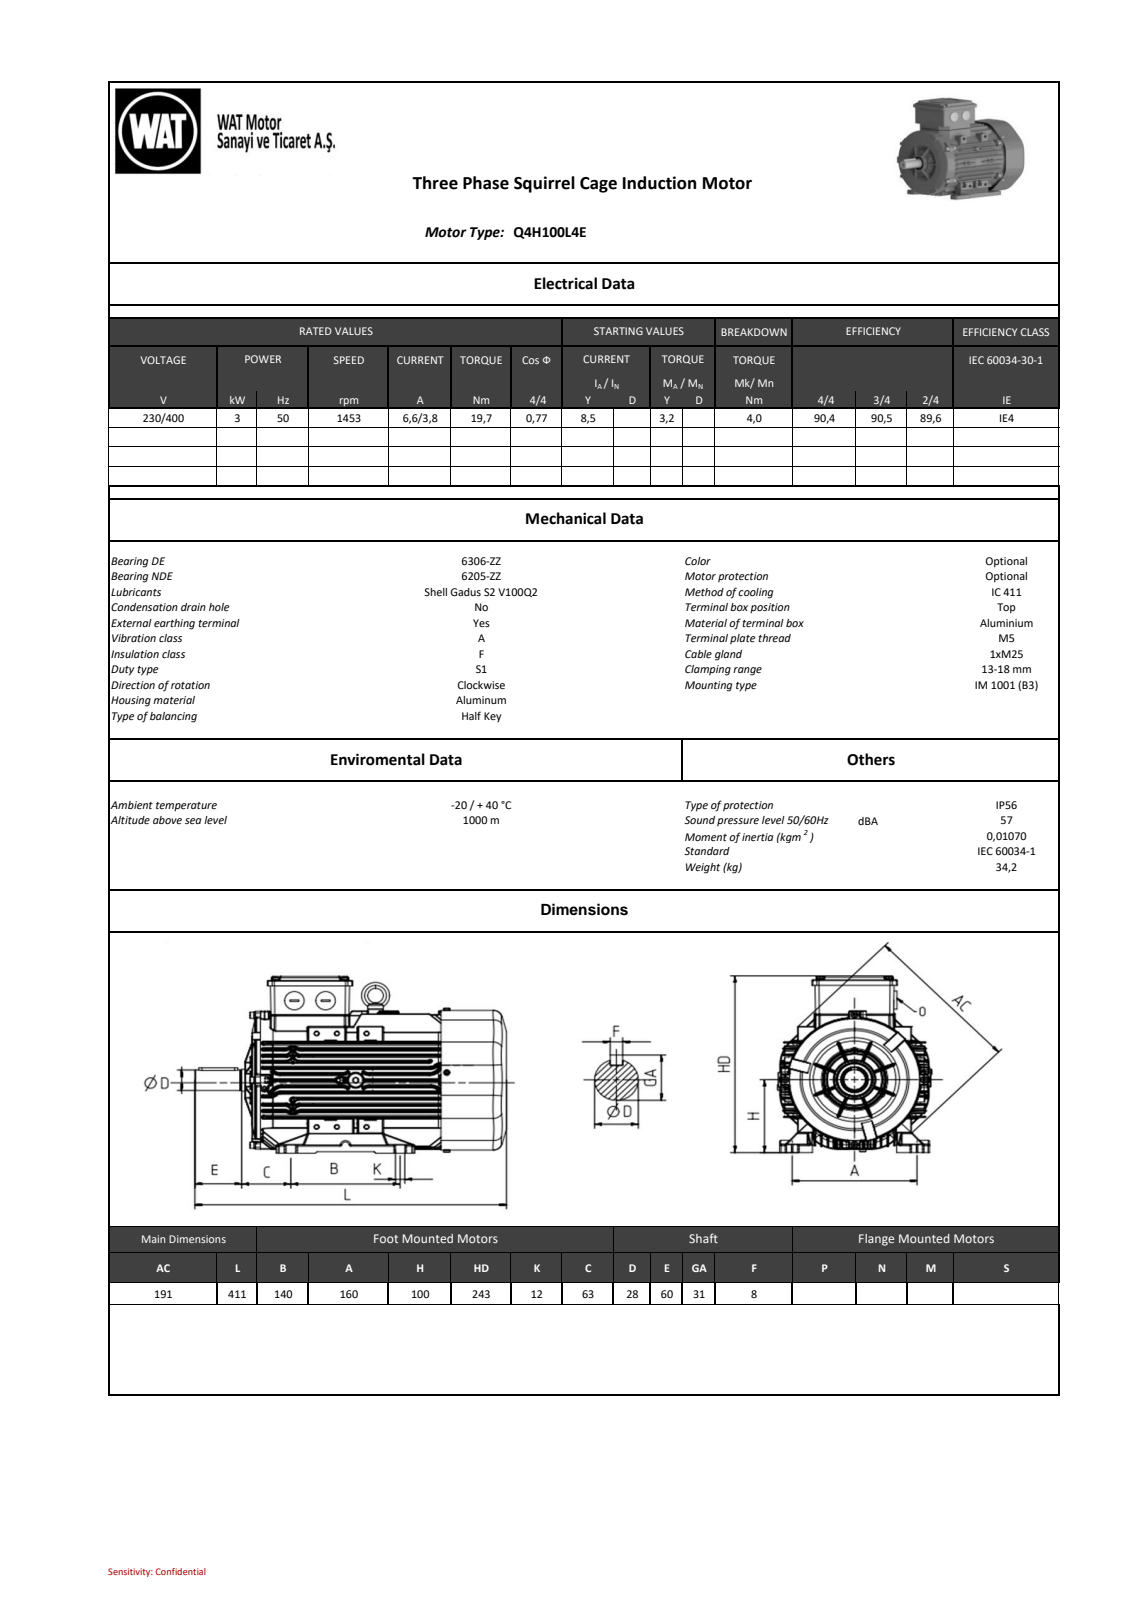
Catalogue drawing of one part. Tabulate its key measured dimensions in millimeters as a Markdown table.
| quantity | value |
| --- | --- |
| part name | AC_objects |
| STEP written by | SIEMENS PLM Software NX2206.8101 (AUTOMOTIVE_DESIGN) |
| units | millimeters |
| bodies | 0 solids, 6507 faces (1493 planar, 1991 cylindrical, 3023 other) |
| overall size | 411.25 × 242.57 × 197.57 |
| round holes (diameter × count) | 6.5 × 4, 4 × 1, 8.5 × 1, 10 × 1, 10.5 × 1, 12 × 1, 43.9 × 1, 44.1 × 1, 48.9 × 1, 49.1 × 1, 52 × 1, 57.4 × 1 |
| round bosses / shafts (diameter × count) | 8 × 8, 12 × 4, 9.2 × 4, 8.28 × 4, 6 × 4, 113.5 × 1, 93.5 × 1, 61 × 1 |
| partial cylindrical surfaces (radius × count) | 0.8 × 587, 1 × 298, 2 × 124, 1.5 × 86, 0.5 × 60, 0.81 × 57, 1.15 × 19, 2.5 × 16 |
| main face-to-face distances | 8.53, 8.46, 8.45, 76.24, 16.91, 93.45, 25.58, 17.05, 76.68, 59.63 |
| hole center spacings | 64, 66.95, 105.32, 128, 143.11 |
